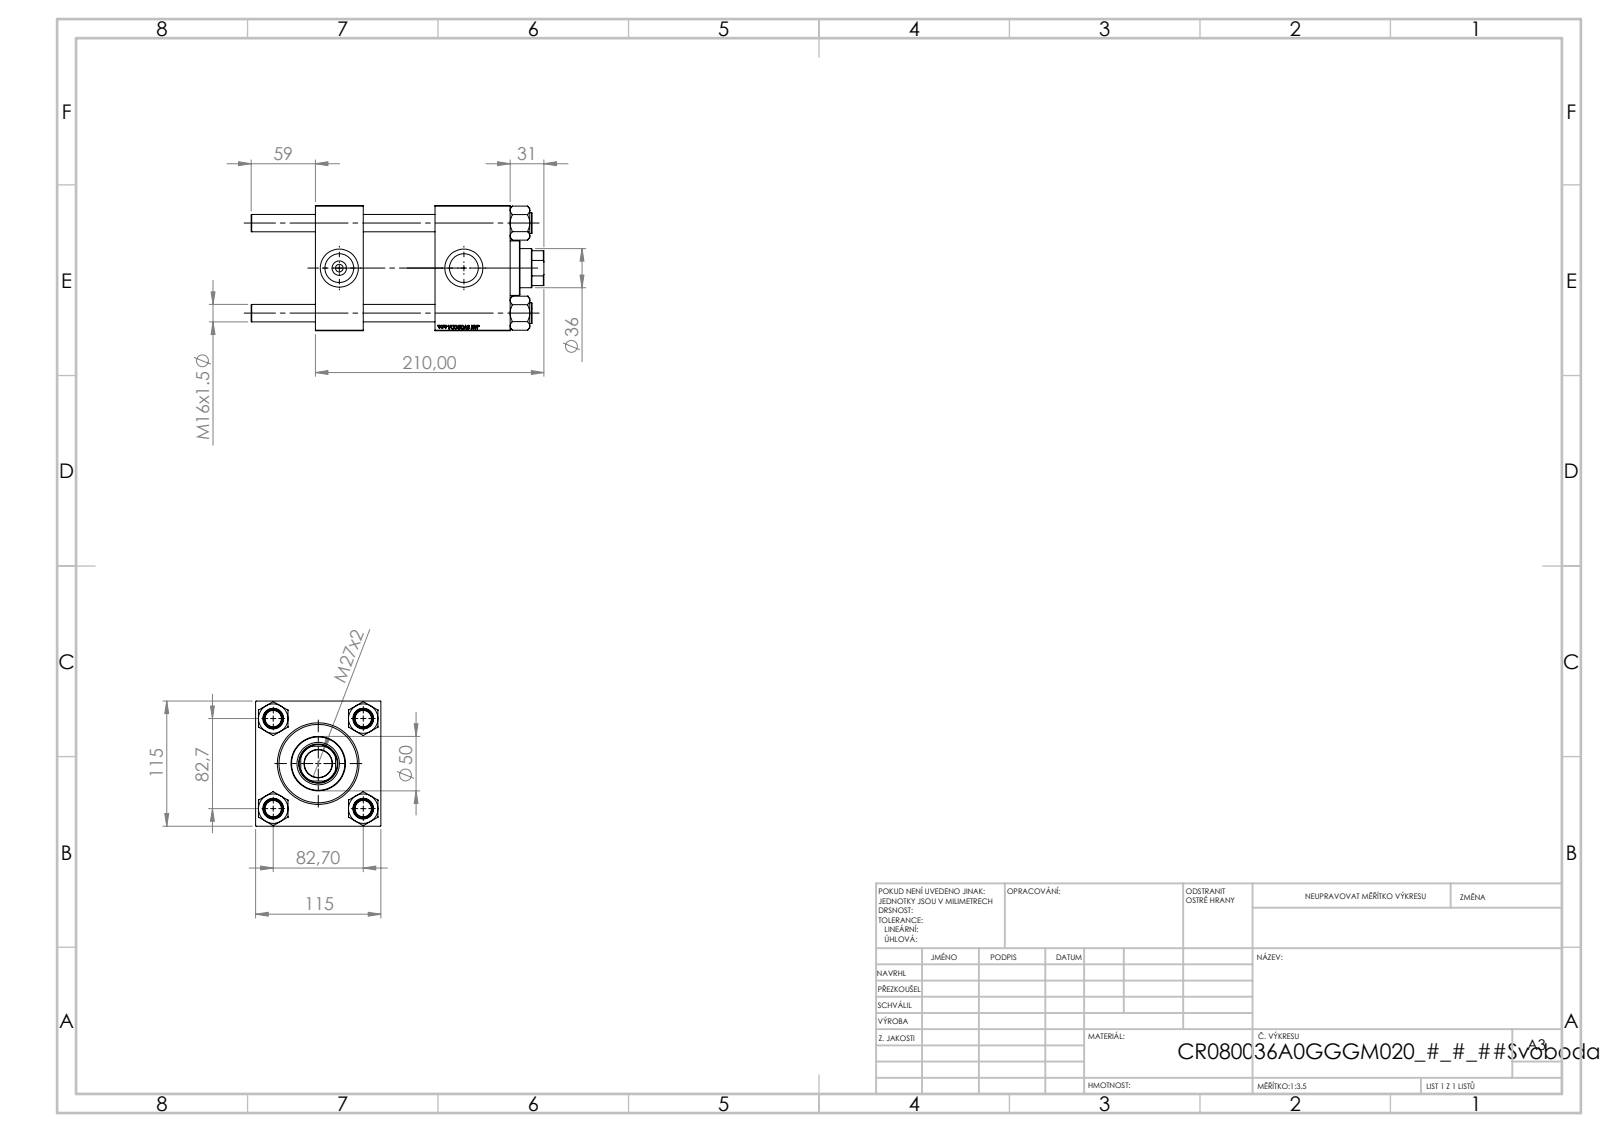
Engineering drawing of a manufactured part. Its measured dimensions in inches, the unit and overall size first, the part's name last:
Units: inches
Overall size (bounding box): 10.591 × 4.528 × 4.528
Round holes (diameter × count): ⌀0.63 ×4, ⌀0.276 ×2, ⌀1.041 ×2, ⌀1.378 ×2, ⌀1.004 ×1, ⌀1.417 ×1, ⌀1.535 ×1, ⌀2.402 ×1, ⌀2.835 ×1, ⌀3.15 ×1
Round bosses / shafts (diameter × count): ⌀0.748 ×4, ⌀3.386 ×1, ⌀1.969 ×1
Partial cylindrical surfaces — rounded edges, fillets, slot ends (radius × count): R0.689 ×1
Main face-to-face distances: 4.528, 1.732, 7.047, 5.315, 4.331, 2.717, 2.598, 0.787, 3.504, 5.917
Hole centre spacings: 2.302, 3.256, 4.605, 4.506
Volume: 113.7 in³ · Surface area: 457.9 in²
Bodies: 11 solids, 1182 faces (567 planar, 79 cylindrical, 536 other)
Part name (STEP PRODUCT): V215_VC_A; V215CR_BODY_A; V215CR_VCP; NUT_M5 (+1 more)
STEP written by: SolidWorks 2019 (CONFIG_CONTROL_DESIGN)
